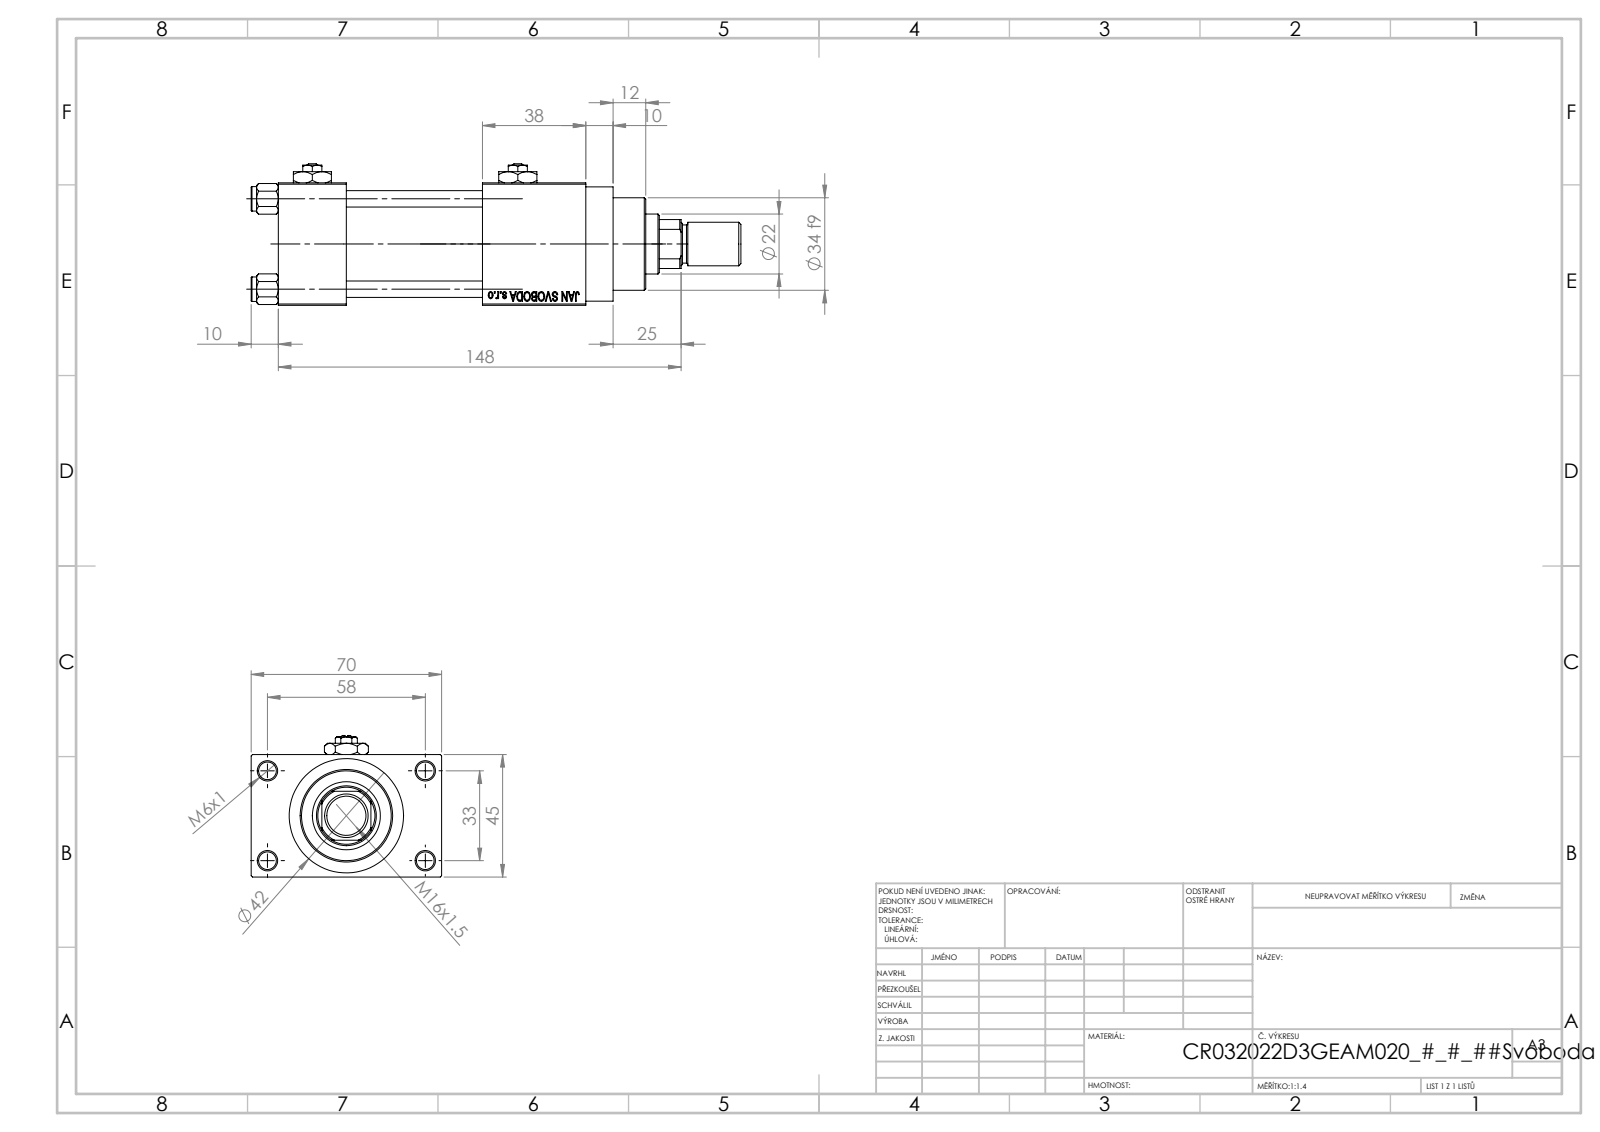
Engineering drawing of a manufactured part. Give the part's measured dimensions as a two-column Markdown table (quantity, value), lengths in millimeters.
| quantity | value |
| --- | --- |
| part name | V215_VC_A; V215CR_D_TYCINKA; NUT_M5_D; Zatka_pro_OIL_PORT (+3 more) |
| STEP written by | SolidWorks 2019 (CONFIG_CONTROL_DESIGN) |
| units | millimeters |
| bodies | 14 solids, 1216 faces (546 planar, 104 cylindrical, 566 other) |
| overall size | 180 × 70 × 52 |
| volume | 247 677 mm³ |
| surface area | 82 741 mm² |
| round holes (diameter × count) | 6 × 4, 6.5 × 4, 7 × 2, 13.16 × 2, 20 × 2, 10.5 × 1, 22 × 1, 24 × 1, 25 × 1, 32 × 1, 33 × 1 |
| round bosses / shafts (diameter × count) | 9 × 4, 42 × 1, 38 × 1, 34 × 1, 16 × 1, 14 × 1 |
| partial cylindrical surfaces (radius × count) | 10.5 × 1 |
| main face-to-face distances | 45, 25, 12.5, 57.5, 50, 75, 88, 70, 38, 113 |
| hole center spacings | 12.4, 23.48, 33.2, 33.37, 35.35, 45.6, 56.35, 33 |
